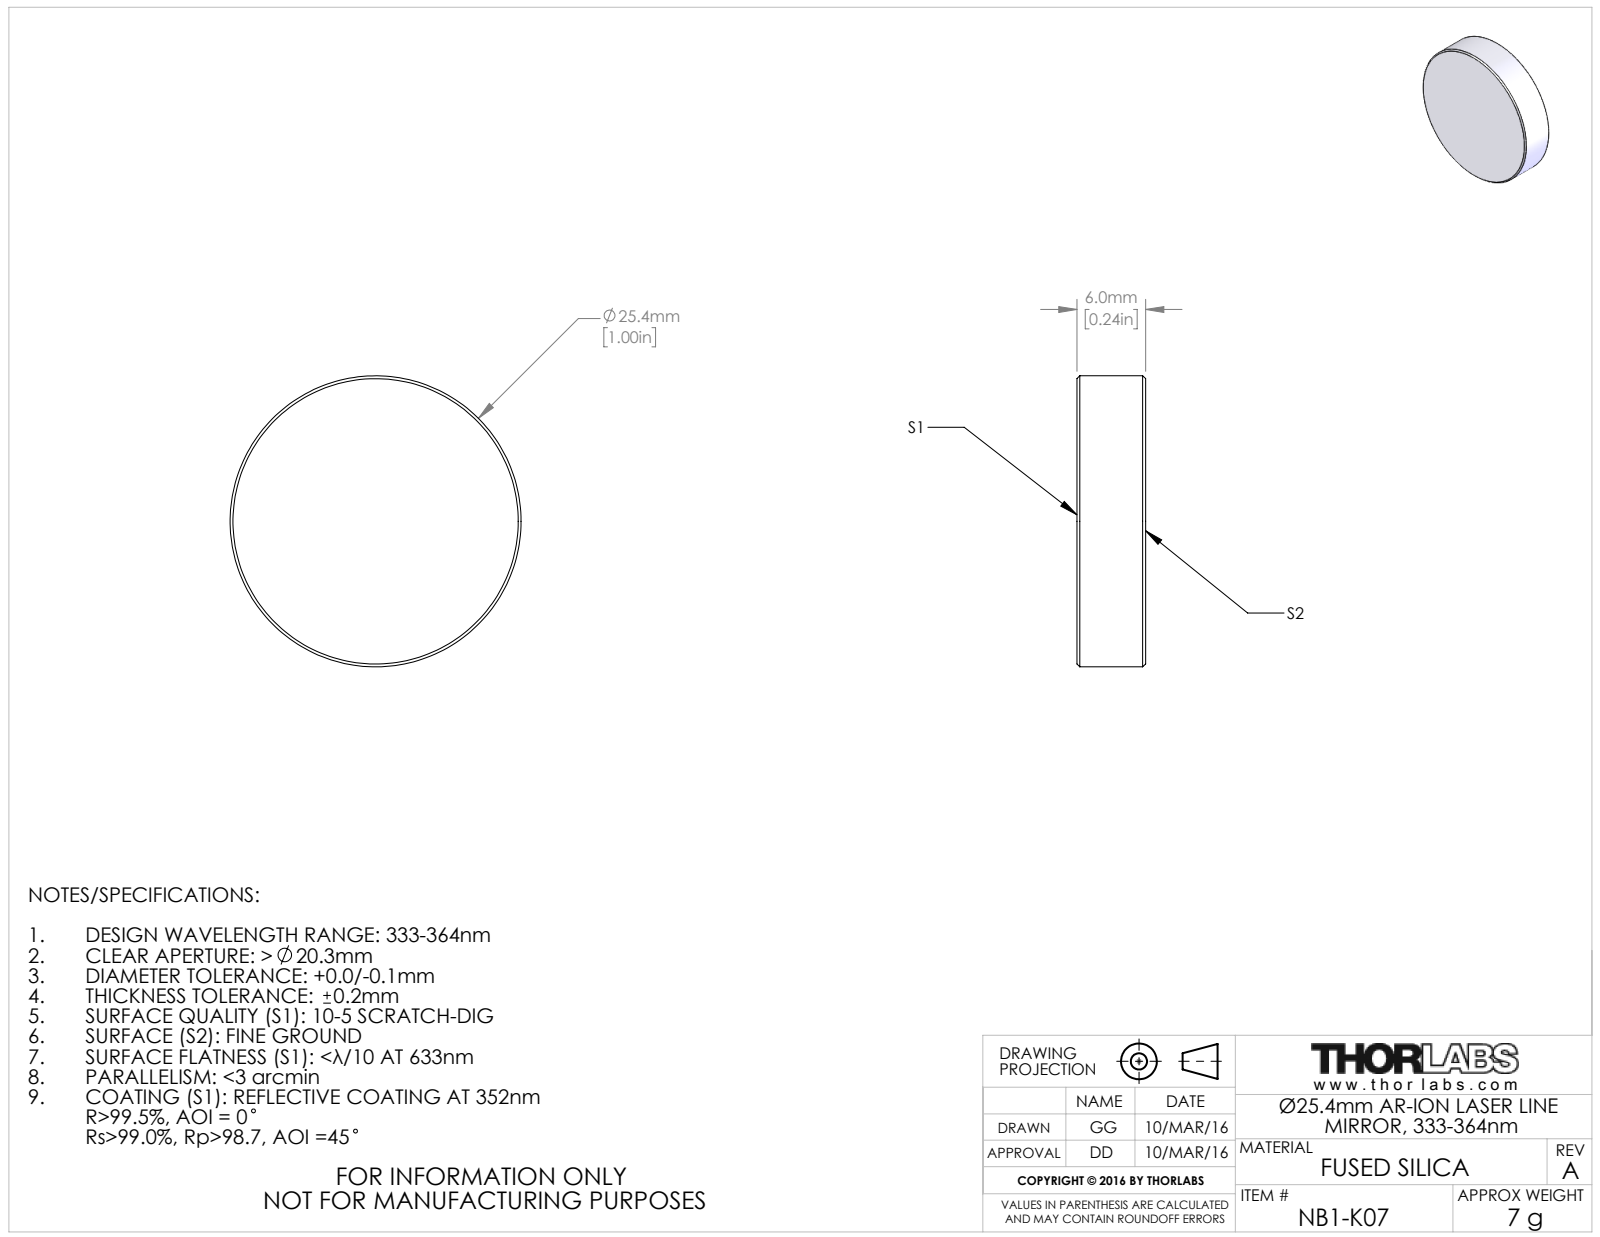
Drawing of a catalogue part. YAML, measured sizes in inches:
part_name: "TTN050491-E0W"
step_written_by: "SolidWorks 2016 (CONFIG_CONTROL_DESIGN)"
units: inches
bodies: {solids: 1, faces: 31, planar: 25, cylindrical: 2, other: 4}
overall_size: [1, 1, 0.236]
volume: 0.185
surface_area: 2.277
round_bosses_or_shafts:
  - {diameter: 1, count: 1}
face_to_face_distances: [0.236]
